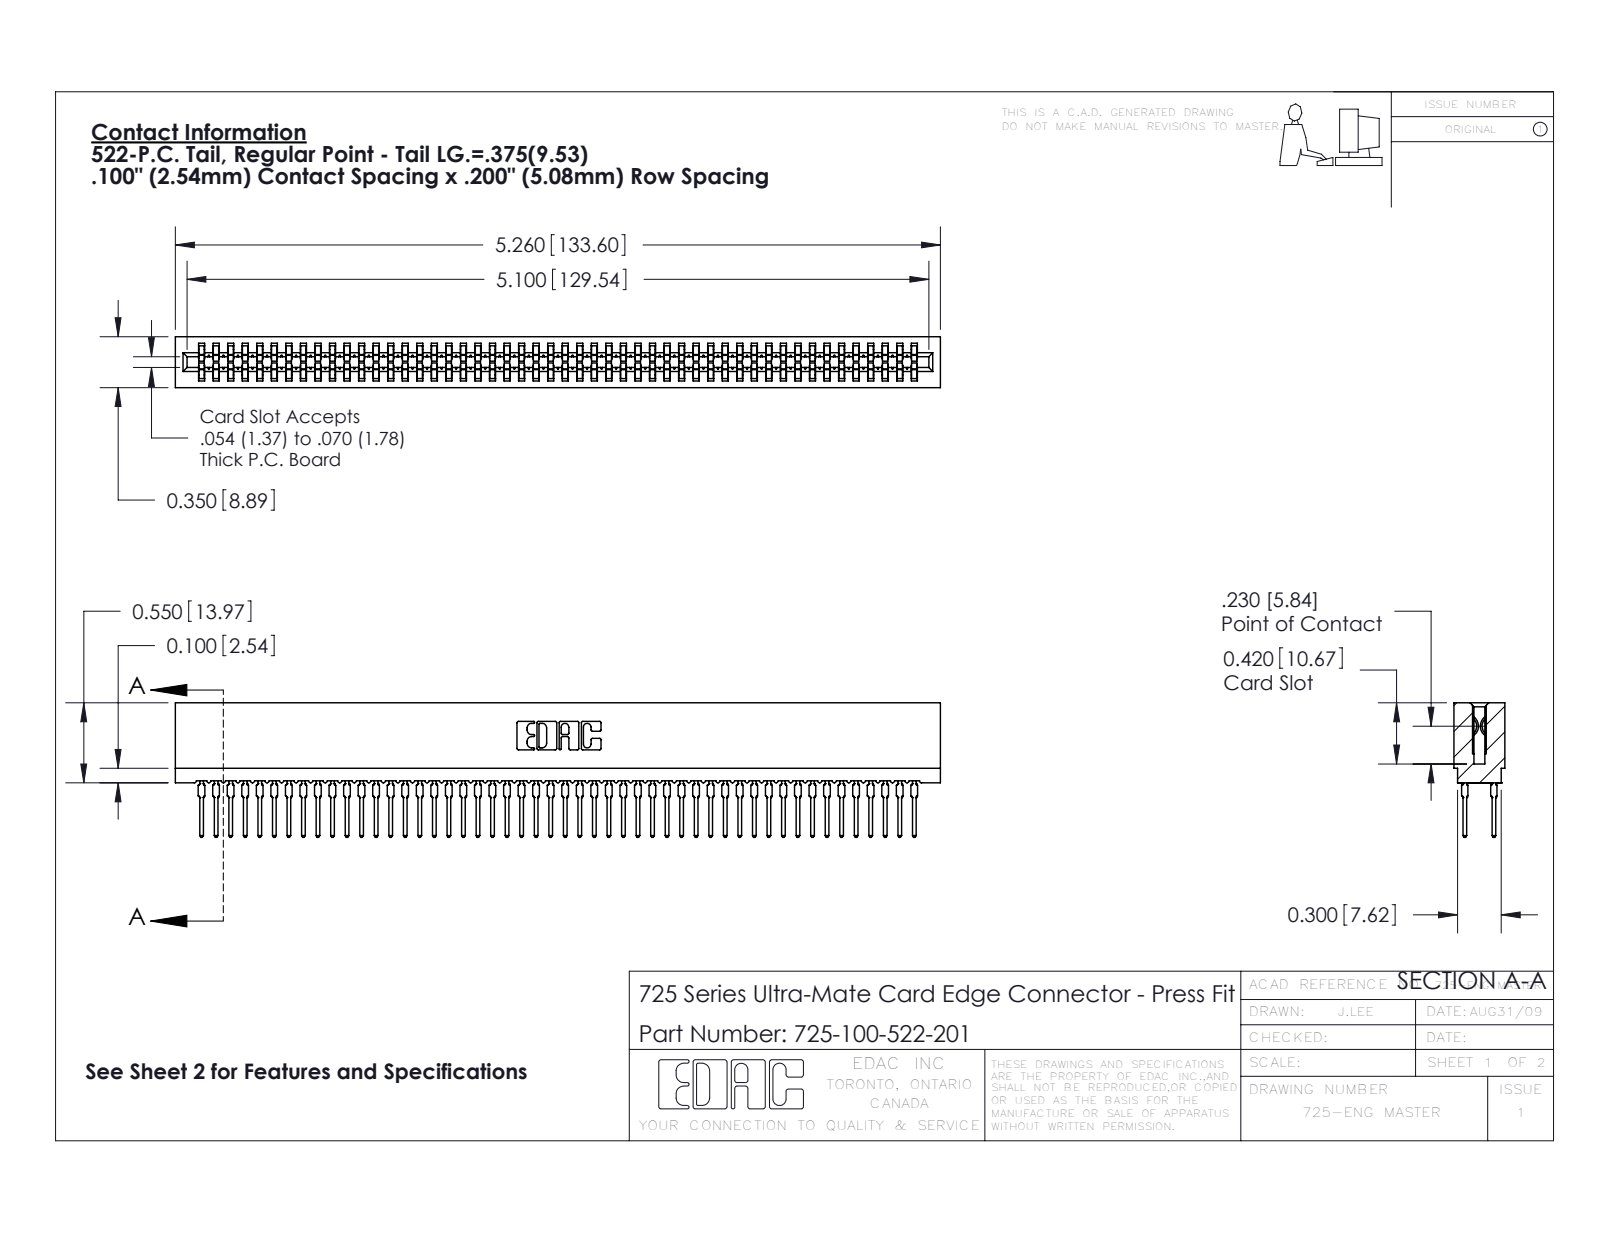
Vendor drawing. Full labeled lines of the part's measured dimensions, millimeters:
Part name (STEP PRODUCT): 745-292-001_522; 725 Part_Insulator Option - 01; 725-100-522-201
STEP written by: SolidWorks 2016 (CONFIG_CONTROL_DESIGN)
Units: millimetres
Bodies: 101 solids, 9045 faces (4655 planar, 1790 cylindrical, 2600 other)
Overall size (bounding box): 133.6 × 23.5 × 8.9
Volume: 10 700 mm³ · Surface area: 23 050 mm²
Partial cylindrical surfaces — rounded edges, fillets, slot ends (radius × count): R0.5 ×200, R0.4 ×100, R0.3 ×22, R0.1 ×8, R0.3 ×8, R0.2 ×6, R0.8 ×6, R0.7 ×3
Main face-to-face distances: 1.6, 7.3, 8.9, 5.1, 5.4, 3.5, 1.9, 3.8, 1.1, 7.7
